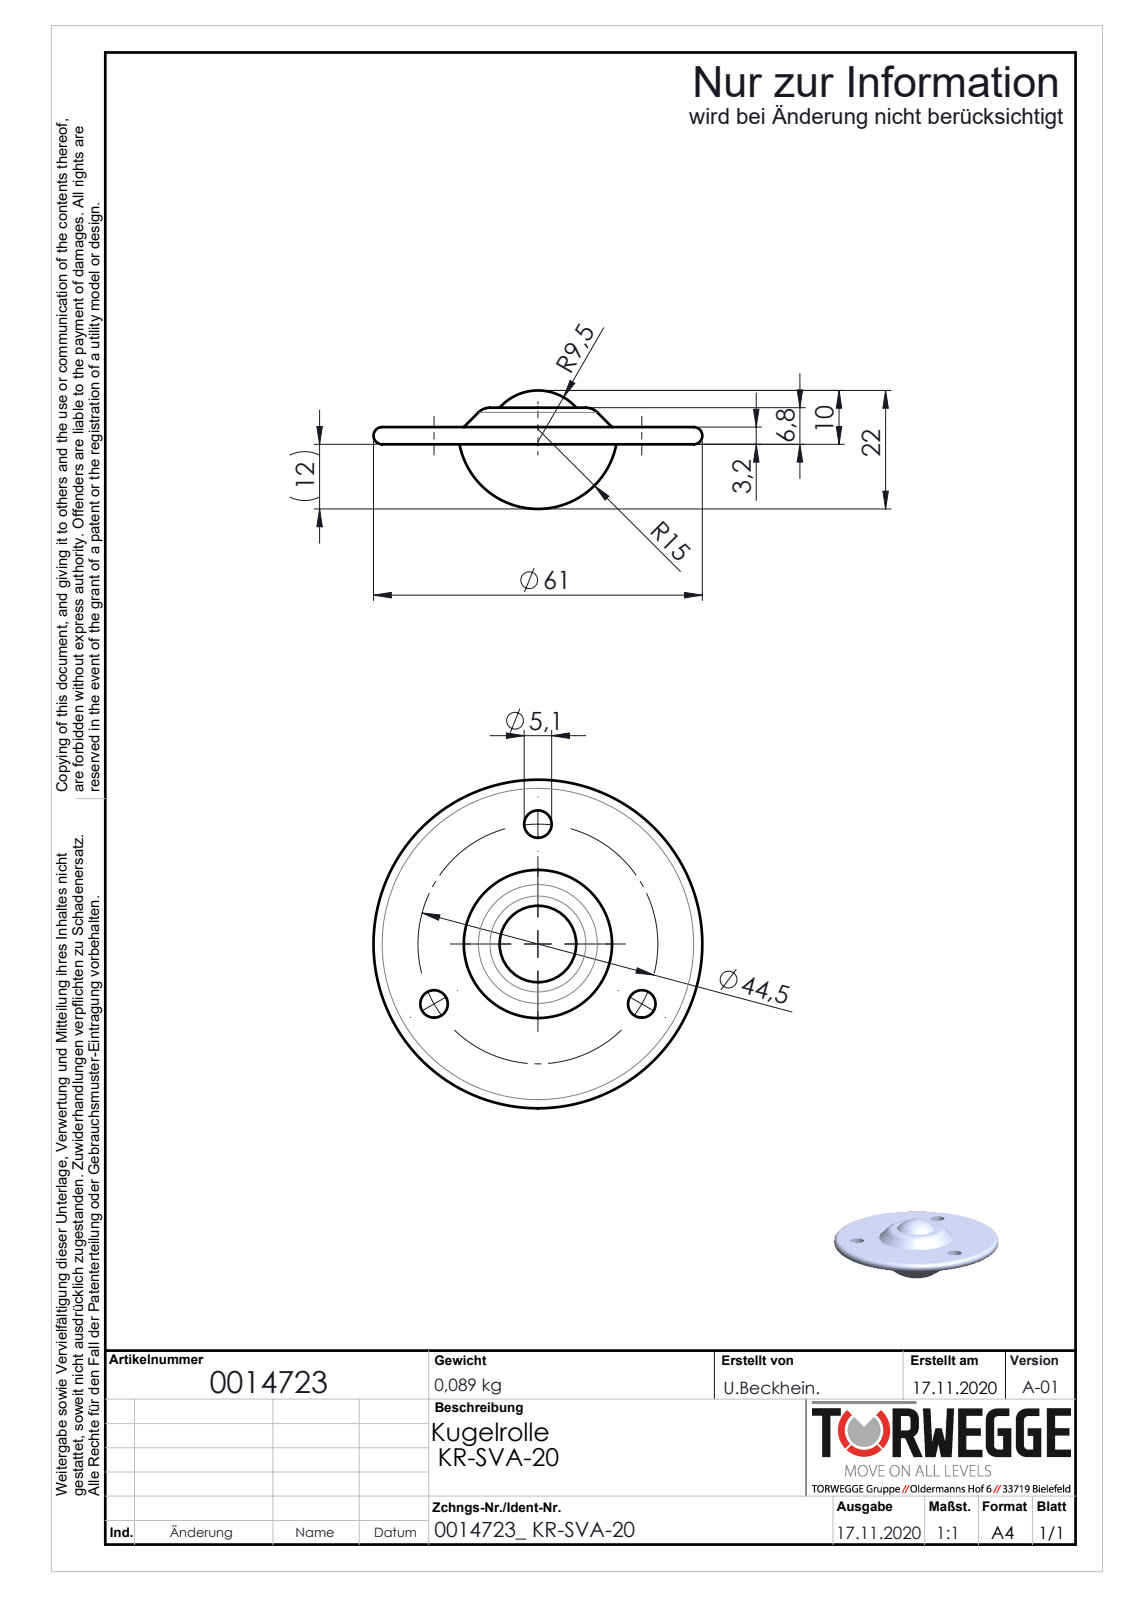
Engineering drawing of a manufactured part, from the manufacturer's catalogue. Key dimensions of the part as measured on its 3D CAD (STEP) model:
Part name (STEP PRODUCT): 0014723
STEP written by: SolidWorks 2018 (AUTOMOTIVE_DESIGN)
Units: millimetres
Bodies: 1 solid, 19 faces (3 planar, 6 cylindrical, 10 other)
Overall size (bounding box): 61 × 61 × 21.52
Volume: 15 730 mm³ · Surface area: 6 811 mm²
Round holes (diameter × count): ⌀5.1 ×3
Main face-to-face distances: 3.2, 6.8, 3.6
Hole centre spacings: 38.53, 38.54
